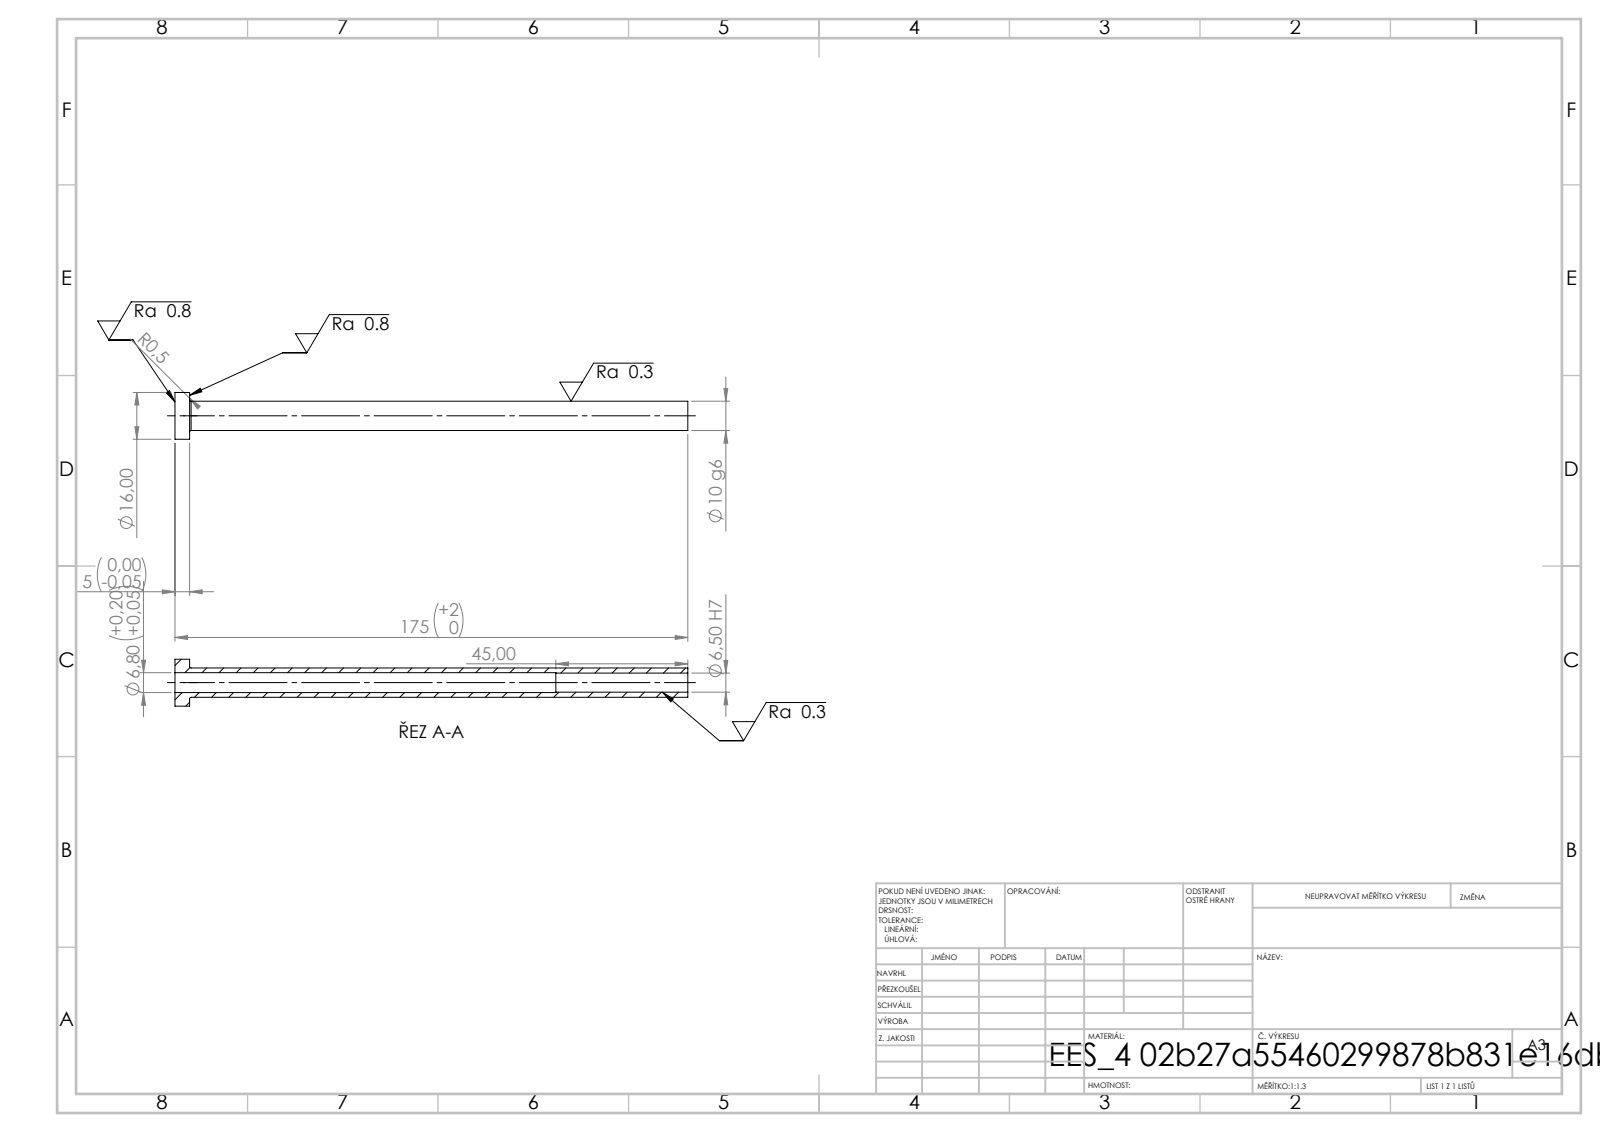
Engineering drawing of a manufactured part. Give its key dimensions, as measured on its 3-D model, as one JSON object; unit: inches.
{"step_written_by": "SolidWorks 2019 (CONFIG_CONTROL_DESIGN)", "units": "inches", "bodies": {"solids": 1, "faces": 14, "planar": 4, "cylindrical": 8, "other": 2}, "overall_size": [6.89, 0.63, 0.63], "volume_in3": 0.497, "surface_area_in2": 14.91, "round_holes": [[0.256, 1], [0.268, 1]], "round_bosses_or_shafts": [[0.63, 1], [0.394, 1]], "face_to_face_distances": [0.197, 6.89, 6.693, 5.118, 4.921, 1.772]}
